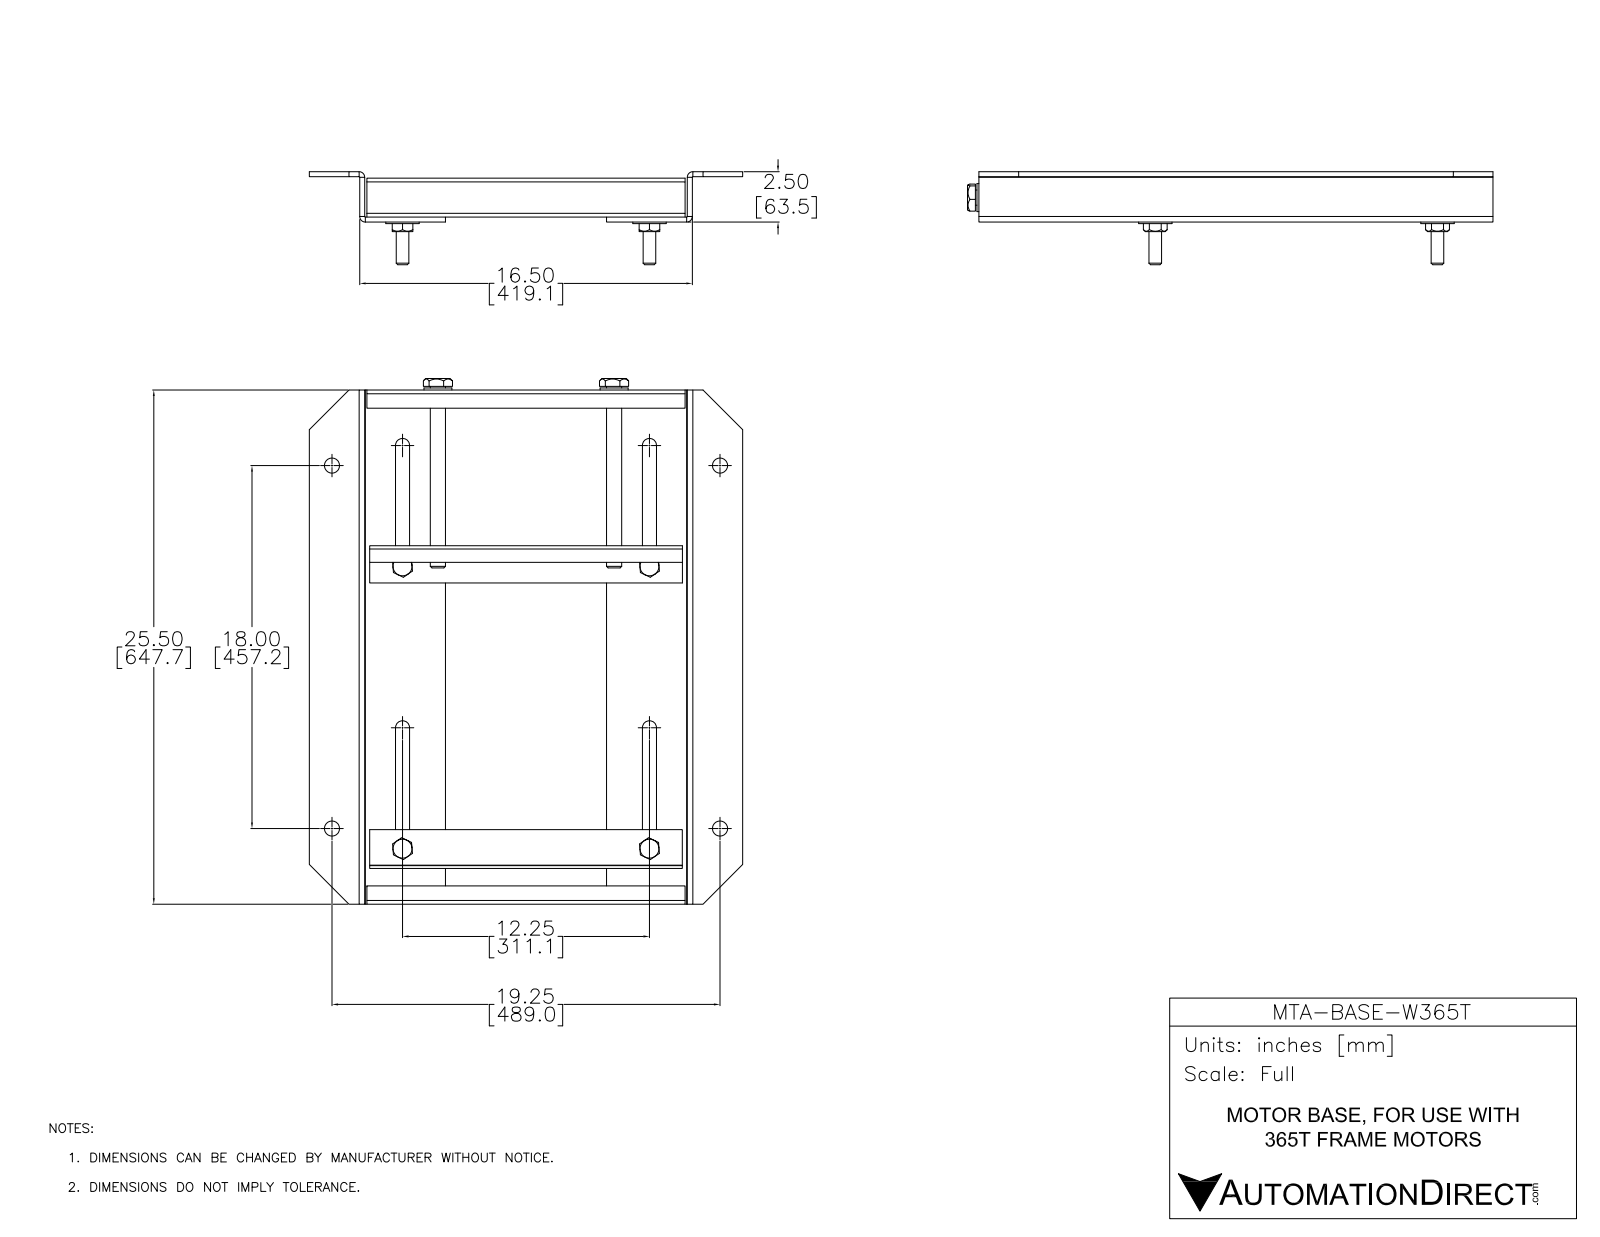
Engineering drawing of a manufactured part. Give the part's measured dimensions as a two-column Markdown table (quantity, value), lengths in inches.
| quantity | value |
| --- | --- |
| part name | W365T |
| STEP written by | SolidWorks 2017 (AUTOMOTIVE_DESIGN) |
| units | inches |
| bodies | 26 solids, 410 faces (224 planar, 110 cylindrical, 76 other) |
| overall size | 26.071 × 21.5 × 4.612 |
| volume | 155.7 in³ |
| surface area | 1 508 in² |
| round holes (diameter × count) | 0.75 × 6, 0.63 × 4, 0.787 × 4, 0.866 × 4, 0.625 × 2, 0.625 × 2, 0.65 × 2 |
| round bosses / shafts (diameter × count) | 1.654 × 4, 1.386 × 2 |
| partial cylindrical surfaces (radius × count) | 0.029 × 11, 0.35 × 8, 0.186 × 4, 0.279 × 4, 0.167 × 3 |
| main face-to-face distances | 0.25, 2.25, 2.5, 2, 0.138, 16.25, 0.157, 2.112, 0.388, 1.862 |
| hole center spacings | 14, 12.25, 8.74, 13.467, 13.467, 18, 18.603, 19.25 |
